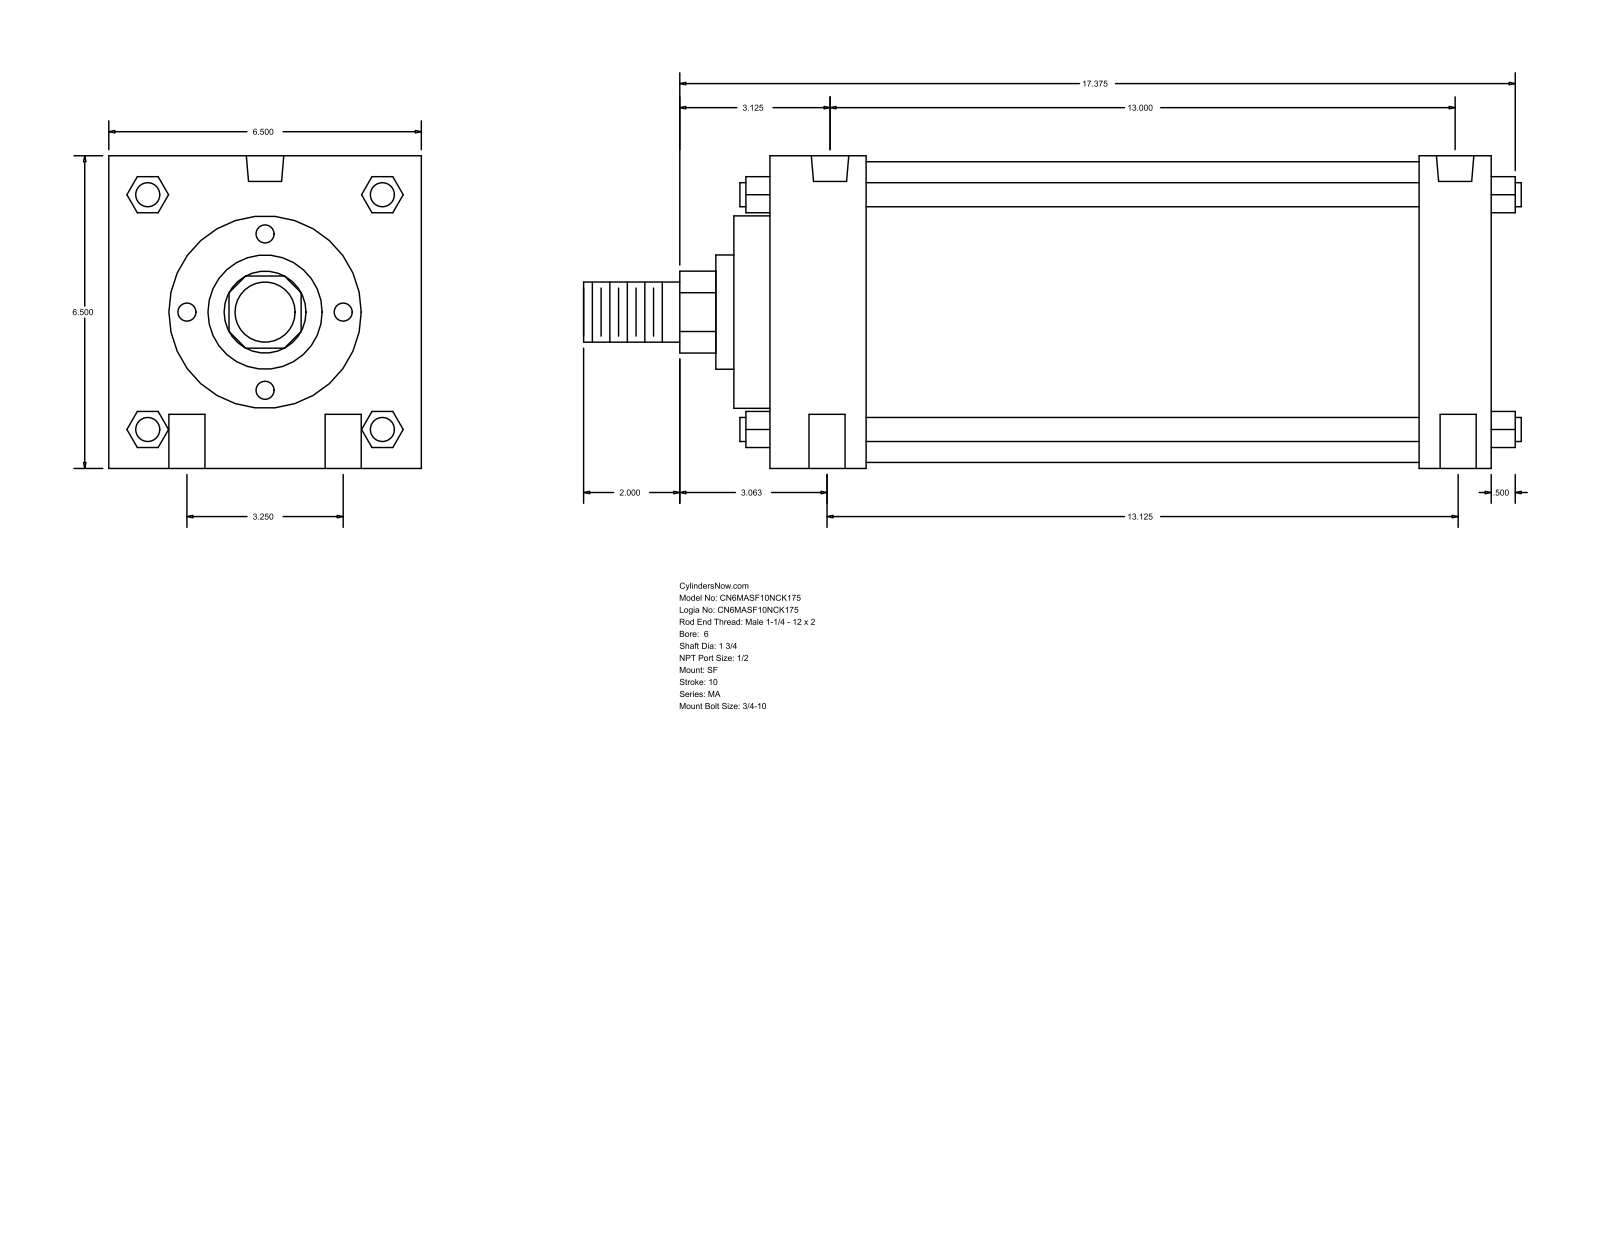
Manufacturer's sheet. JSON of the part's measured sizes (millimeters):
{"part_name": "MA_SF__0600_1.75", "step_written_by": "GSSL Pune (CONFIG_CONTROL_DESIGN)", "units": "millimeters", "bodies": {"solids": 0, "faces": 126, "planar": 95, "cylindrical": 31, "other": 0}, "overall_size": [495.3, 165.1, 165.1], "round_holes": [[19.05, 4], [17.46, 2], [19.77, 2]], "round_bosses_or_shafts": [[12.7, 4], [158.75, 1], [101.6, 1], [60.33, 1], [44.45, 1], [31.75, 1]], "partial_cylinders_radius": [[21.63, 1]], "face_to_face_distances": [165.1, 381, 19.05, 50.8, 342.9, 38.1, 292.1, 330.2, 69.85, 361.95], "hole_center_spacings": [41.3, 334.34, 82.54, 330.19, 333.37, 343.44]}
